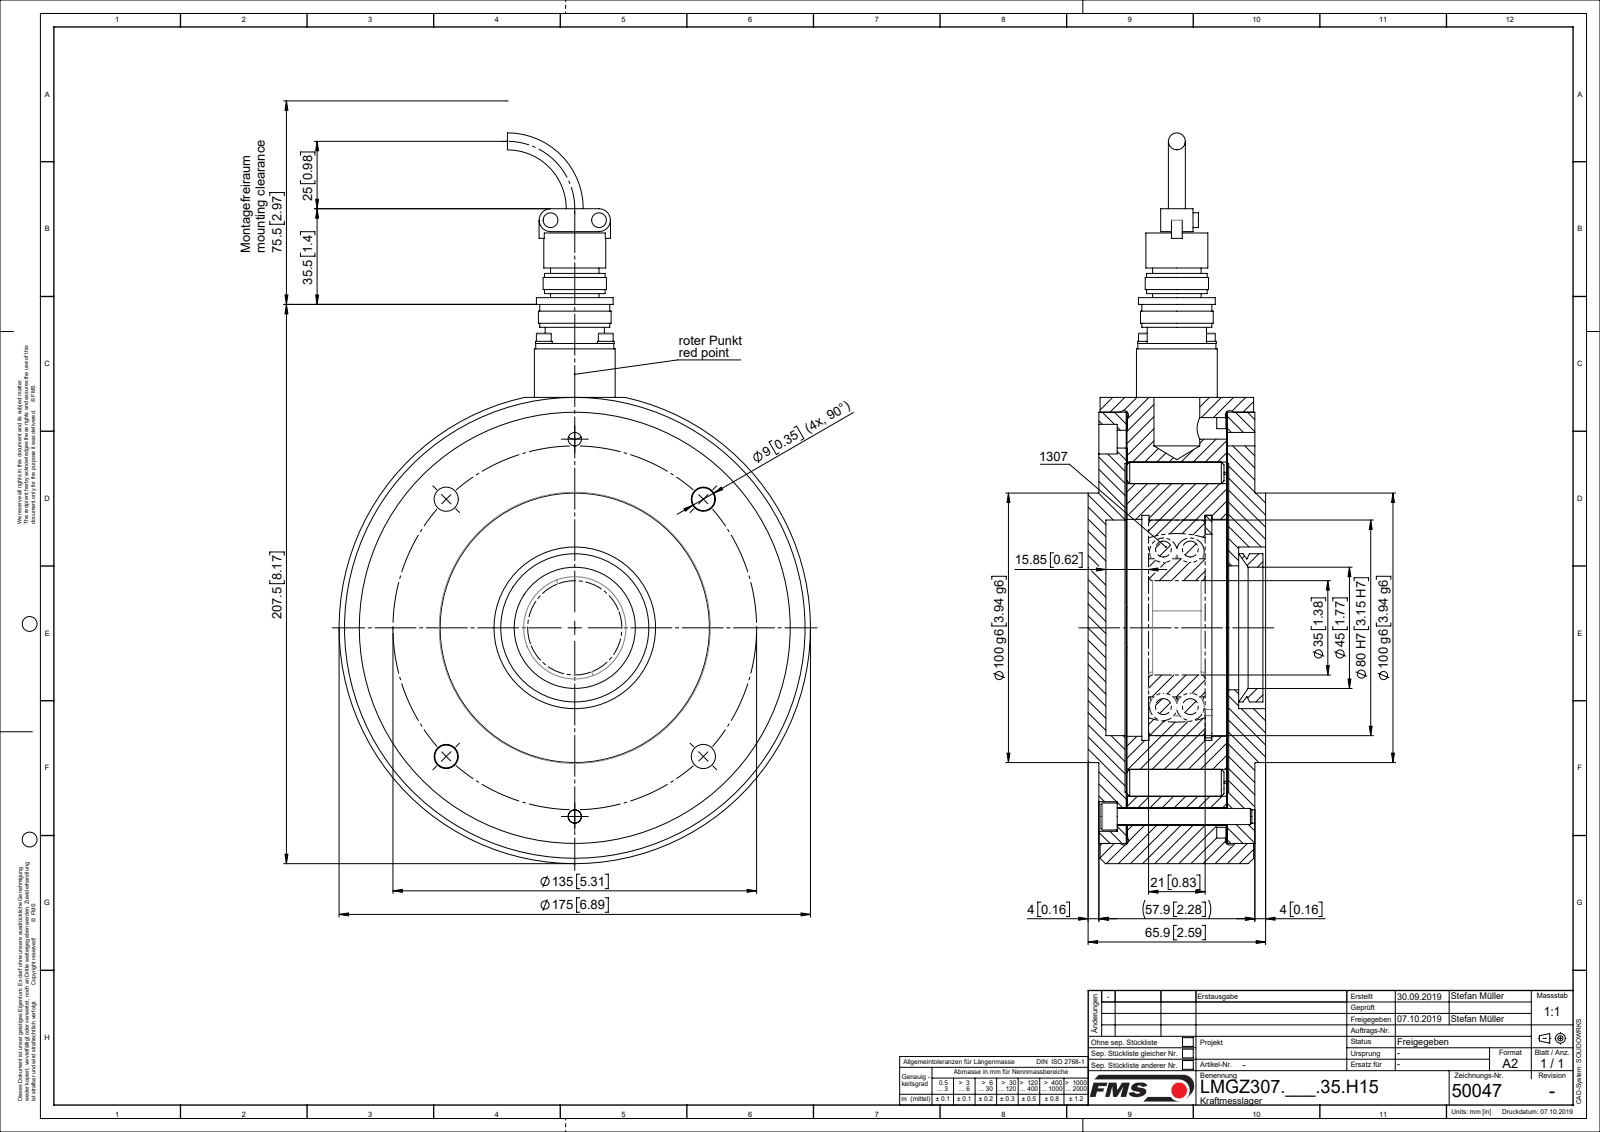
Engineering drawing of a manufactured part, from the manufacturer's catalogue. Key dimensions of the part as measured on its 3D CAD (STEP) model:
Part name (STEP PRODUCT): L50047; L4943004; TEIL1; L48573 (+8 more)
STEP written by: Mechanical Desktop 2007 (CONFIG_CONTROL_DESIGN)
Units: millimetres
Bodies: 19 solids, 366 faces (97 planar, 221 cylindrical, 48 other)
Overall size (bounding box): 413.65 × 175 × 104.7
Volume: 1 285 000 mm³ · Surface area: 264 597 mm²
Round holes (diameter × count): ⌀2.6 ×4, ⌀3.2 ×4, ⌀3.4 ×4, ⌀9 ×4, ⌀5 ×2, ⌀6.6 ×2, ⌀8.68 ×2, ⌀11 ×2, ⌀23 ×1, ⌀35 ×1, ⌀44 ×1, ⌀46 ×1
Round bosses / shafts (diameter × count): ⌀5.5 ×6, ⌀6.2 ×4, ⌀3 ×4, ⌀2.5 ×4, ⌀175 ×1, ⌀160 ×1, ⌀100 ×1, ⌀54 ×1
Partial cylindrical surfaces — rounded edges, fillets, slot ends (radius × count): R4.25 ×2, R7.5 ×2
Main face-to-face distances: 37.25, 10.2, 10.45, 47.45, 47.7, 37, 0.5, 38, 9.7, 48.2
Hole centre spacings: 16.26, 23, 52.67, 67.5, 95.46, 127.04, 32.53, 70
